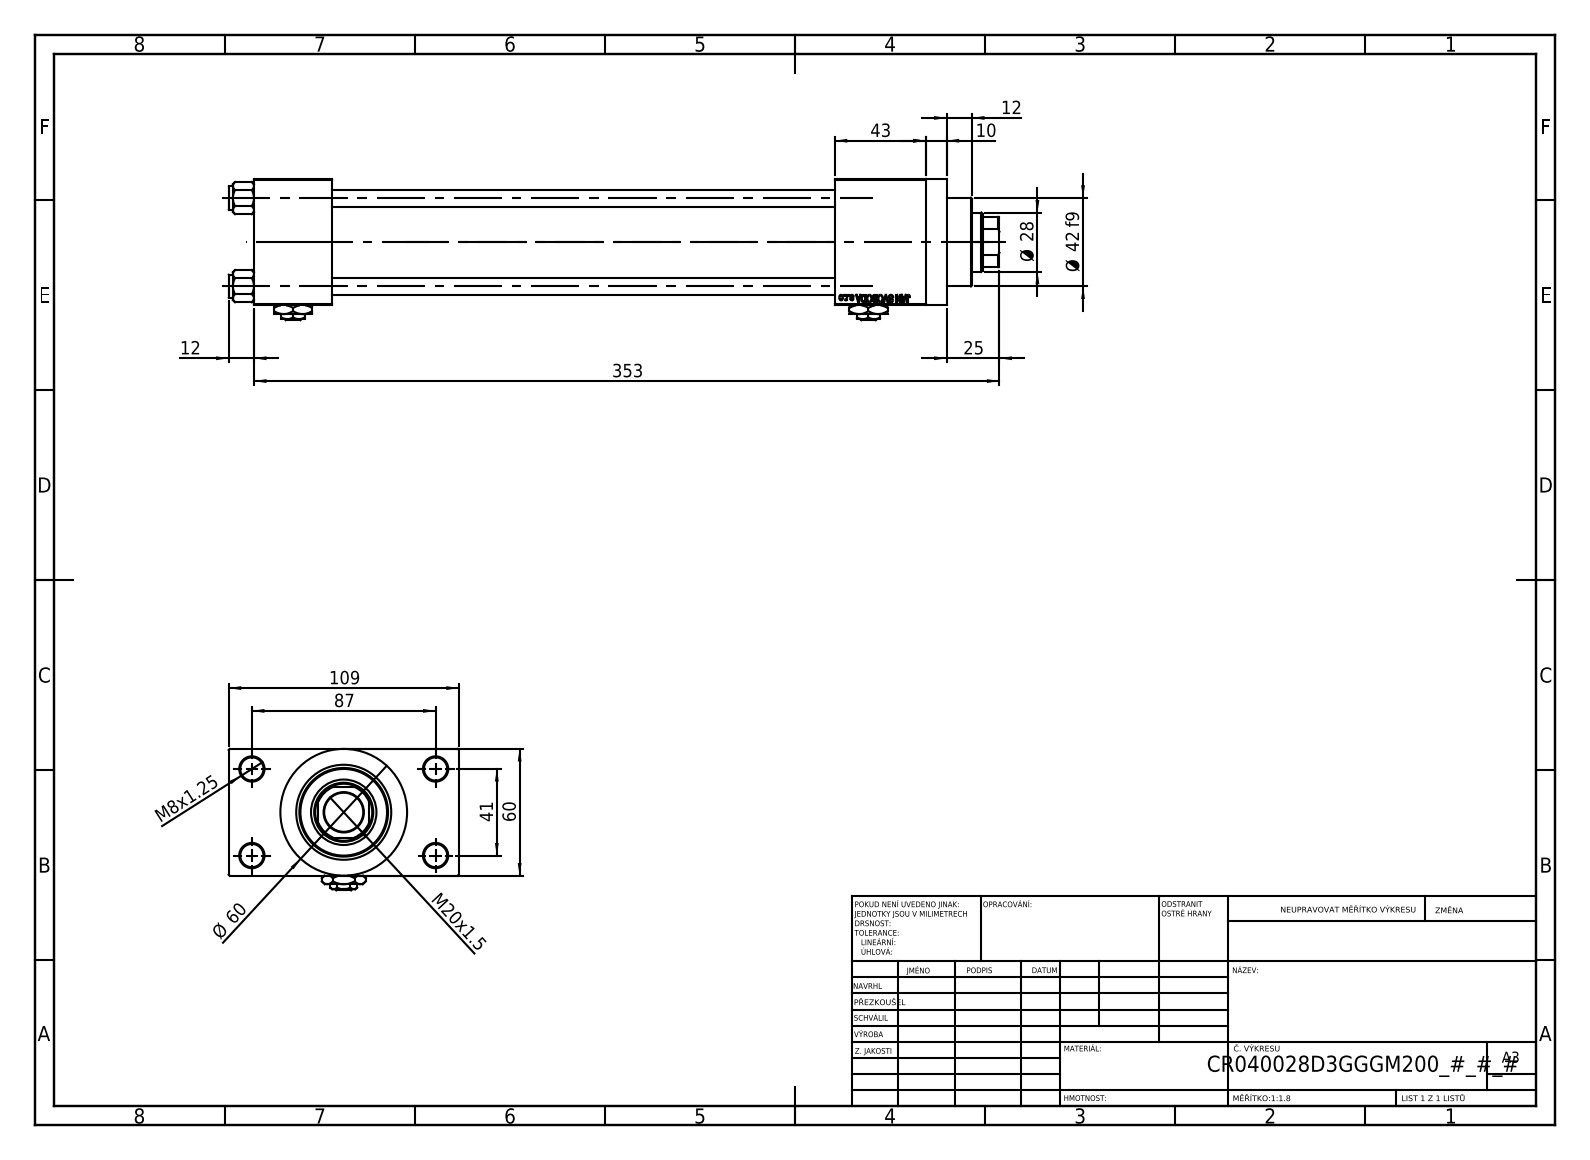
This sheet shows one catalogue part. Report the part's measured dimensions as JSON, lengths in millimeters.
{"part_name": "V215CR_D_Body; NUT_M5_D; V215CR_D_TYCINKA; V215CR_VCP_D (+2 more)", "step_written_by": "SolidWorks 2019 (CONFIG_CONTROL_DESIGN)", "units": "millimeters", "bodies": {"solids": 13, "faces": 1206, "planar": 546, "cylindrical": 100, "other": 560}, "overall_size": [365, 109, 67], "volume_mm3": 751920, "surface_area_mm2": 213036, "round_holes": [[8, 4], [11, 4], [7, 2], [16.66, 2], [24, 2], [18.5, 1], [28, 1], [31, 1], [40, 1], [45, 1]], "round_bosses_or_shafts": [[11, 4], [60, 1], [46, 1], [42, 1]], "partial_cylinders_radius": [[13.5, 1]], "face_to_face_distances": [60, 24.5, 84.5, 238, 37, 275, 318, 281, 43, 109], "hole_center_spacings": [22.65, 29.49, 41.7, 47.15, 48.09, 64.35, 76.49, 41]}
